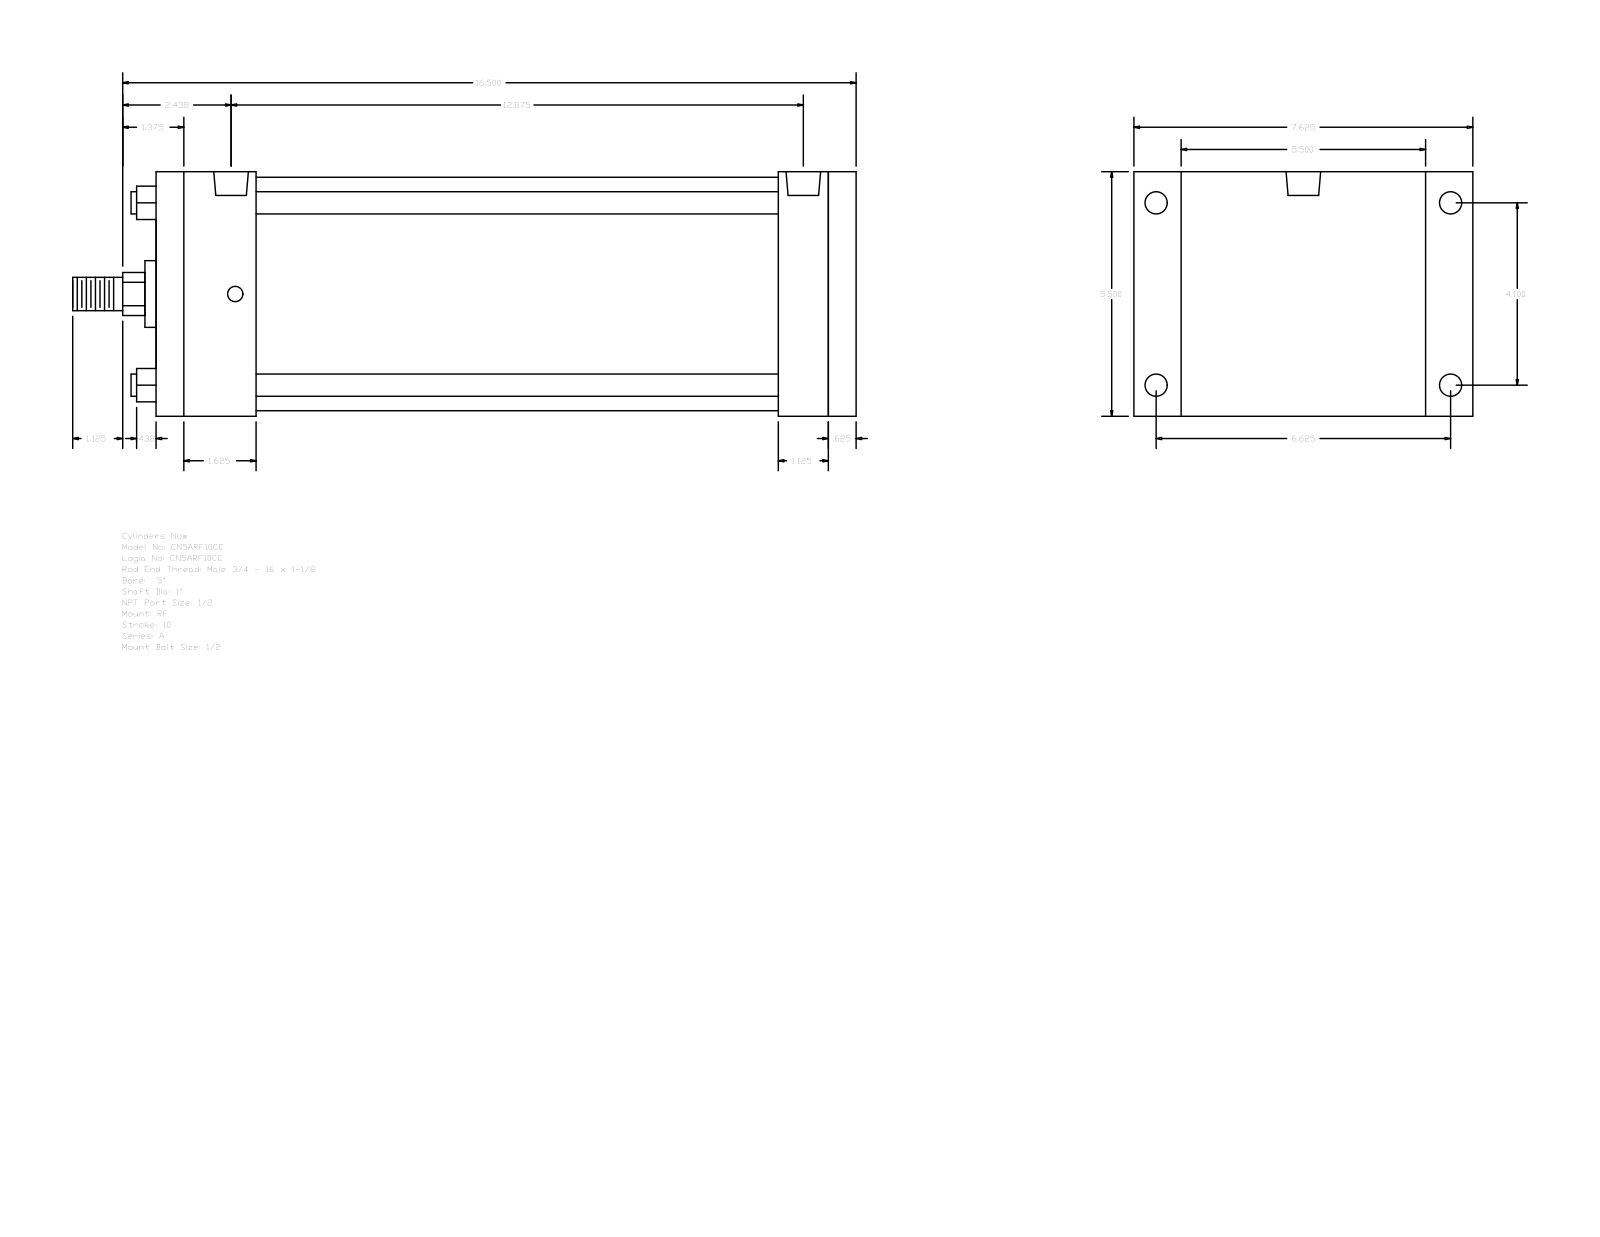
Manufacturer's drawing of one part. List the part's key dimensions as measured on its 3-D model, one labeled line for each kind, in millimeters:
Part name (STEP PRODUCT): A_RF__0500_1
STEP written by: GSSL Pune (CONFIG_CONTROL_DESIGN)
Units: millimetres
Bodies: 0 solids, 92 faces (64 planar, 28 cylindrical, 0 other)
Overall size (bounding box): 447.68 × 193.68 × 139.7
Round holes (diameter × count): ⌀8.73 ×4, ⌀12.7 ×4, ⌀19.77 ×2
Round bosses / shafts (diameter × count): ⌀12.7 ×4, ⌀133.35 ×1, ⌀38.1 ×1, ⌀25.4 ×1, ⌀19.05 ×1
Partial cylindrical surfaces — rounded edges, fillets, slot ends (radius × count): R12.29 ×1
Main face-to-face distances: 139.7, 400.05, 384.18, 15.87, 57.15, 327.03, 342.9, 355.6, 298.45, 28.58
Hole centre spacings: 2.39, 104.14, 168.28, 197.9, 322.25, 324.64, 327.03
